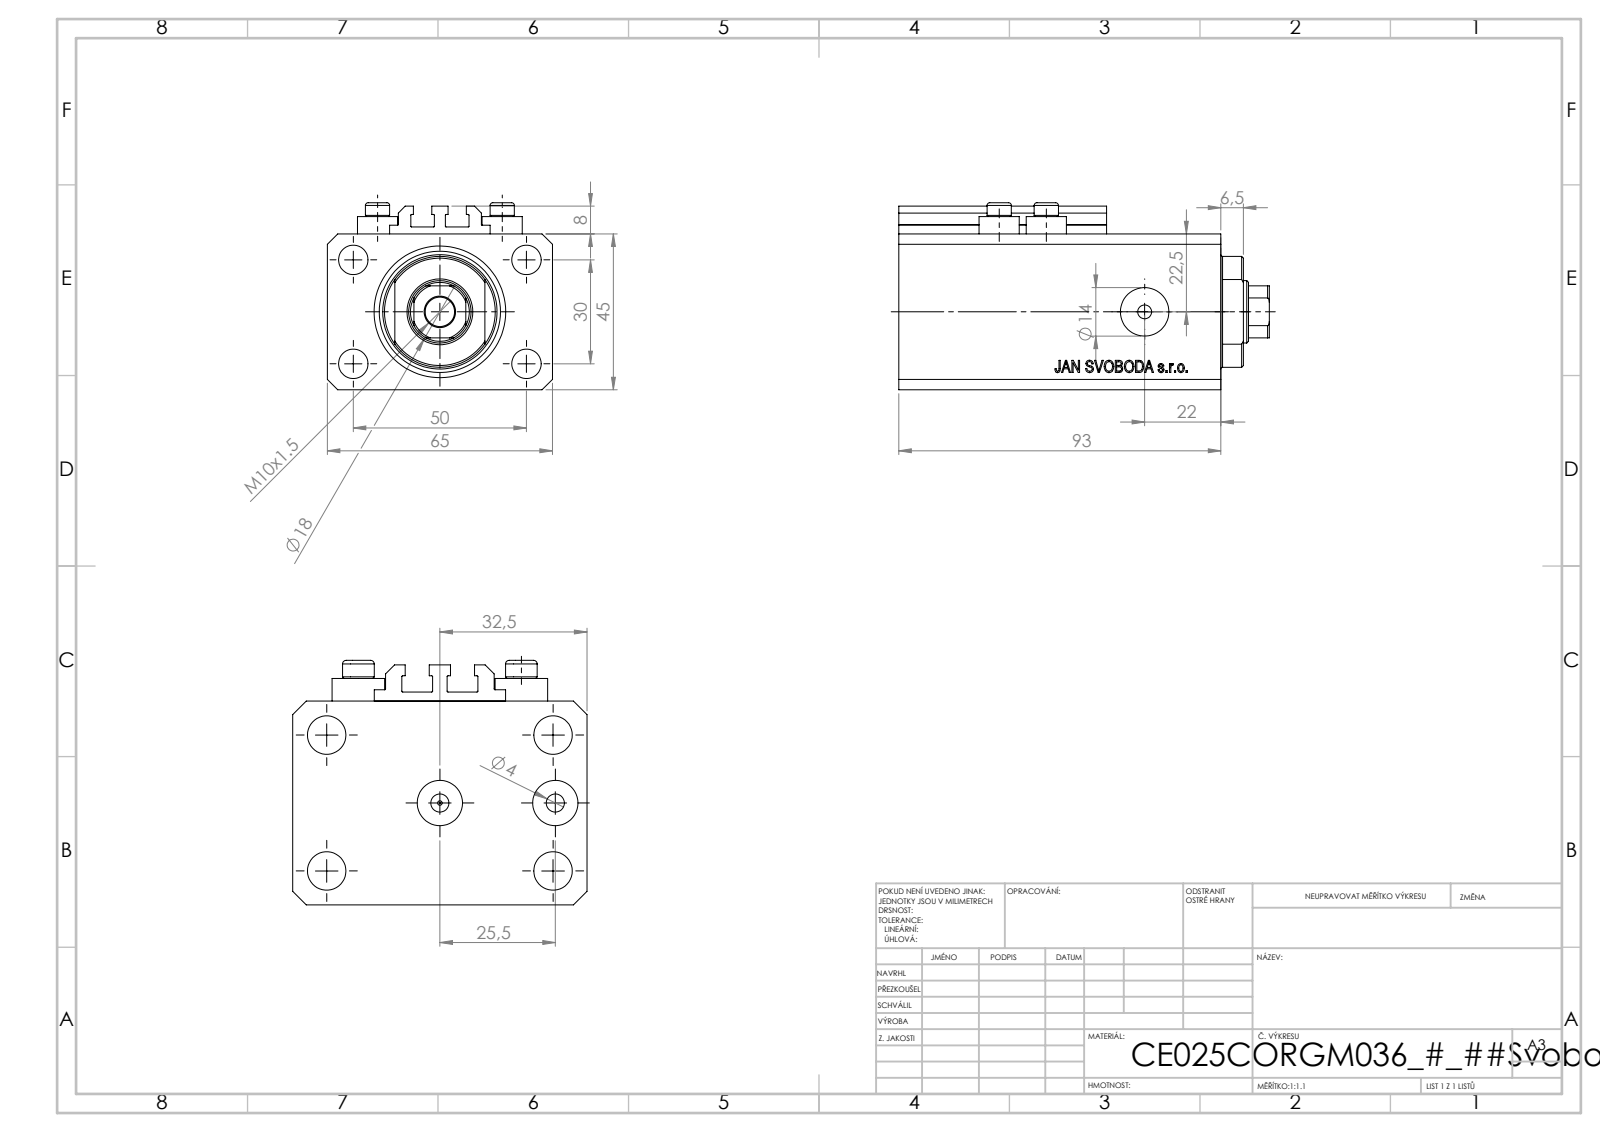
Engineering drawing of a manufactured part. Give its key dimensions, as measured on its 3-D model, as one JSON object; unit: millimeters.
{"part_name": "V250CE_C_VCP; ALLEN BOLT V250CE; V250CE_VC_C; V250CE_C_Body", "step_written_by": "SolidWorks 2019 (CONFIG_CONTROL_DESIGN)", "units": "millimeters", "bodies": {"solids": 8, "faces": 1038, "planar": 504, "cylindrical": 88, "other": 446}, "overall_size": [107, 65, 54], "volume_mm3": 252575, "surface_area_mm2": 66635, "round_holes": [[4, 8], [8.5, 5], [10, 2], [14, 2], [1.25, 1], [18, 1], [25, 1], [38, 1]], "round_bosses_or_shafts": [[11.6, 4], [7, 4]], "partial_cylinders_radius": [[0.2, 10], [8.5, 1], [16, 1]], "face_to_face_distances": [45, 65, 14, 93, 79, 47, 6.9, 72.1, 86.1, 3], "hole_center_spacings": [29.15, 13.6, 15.01, 30, 36, 38.48, 50, 52.68]}
